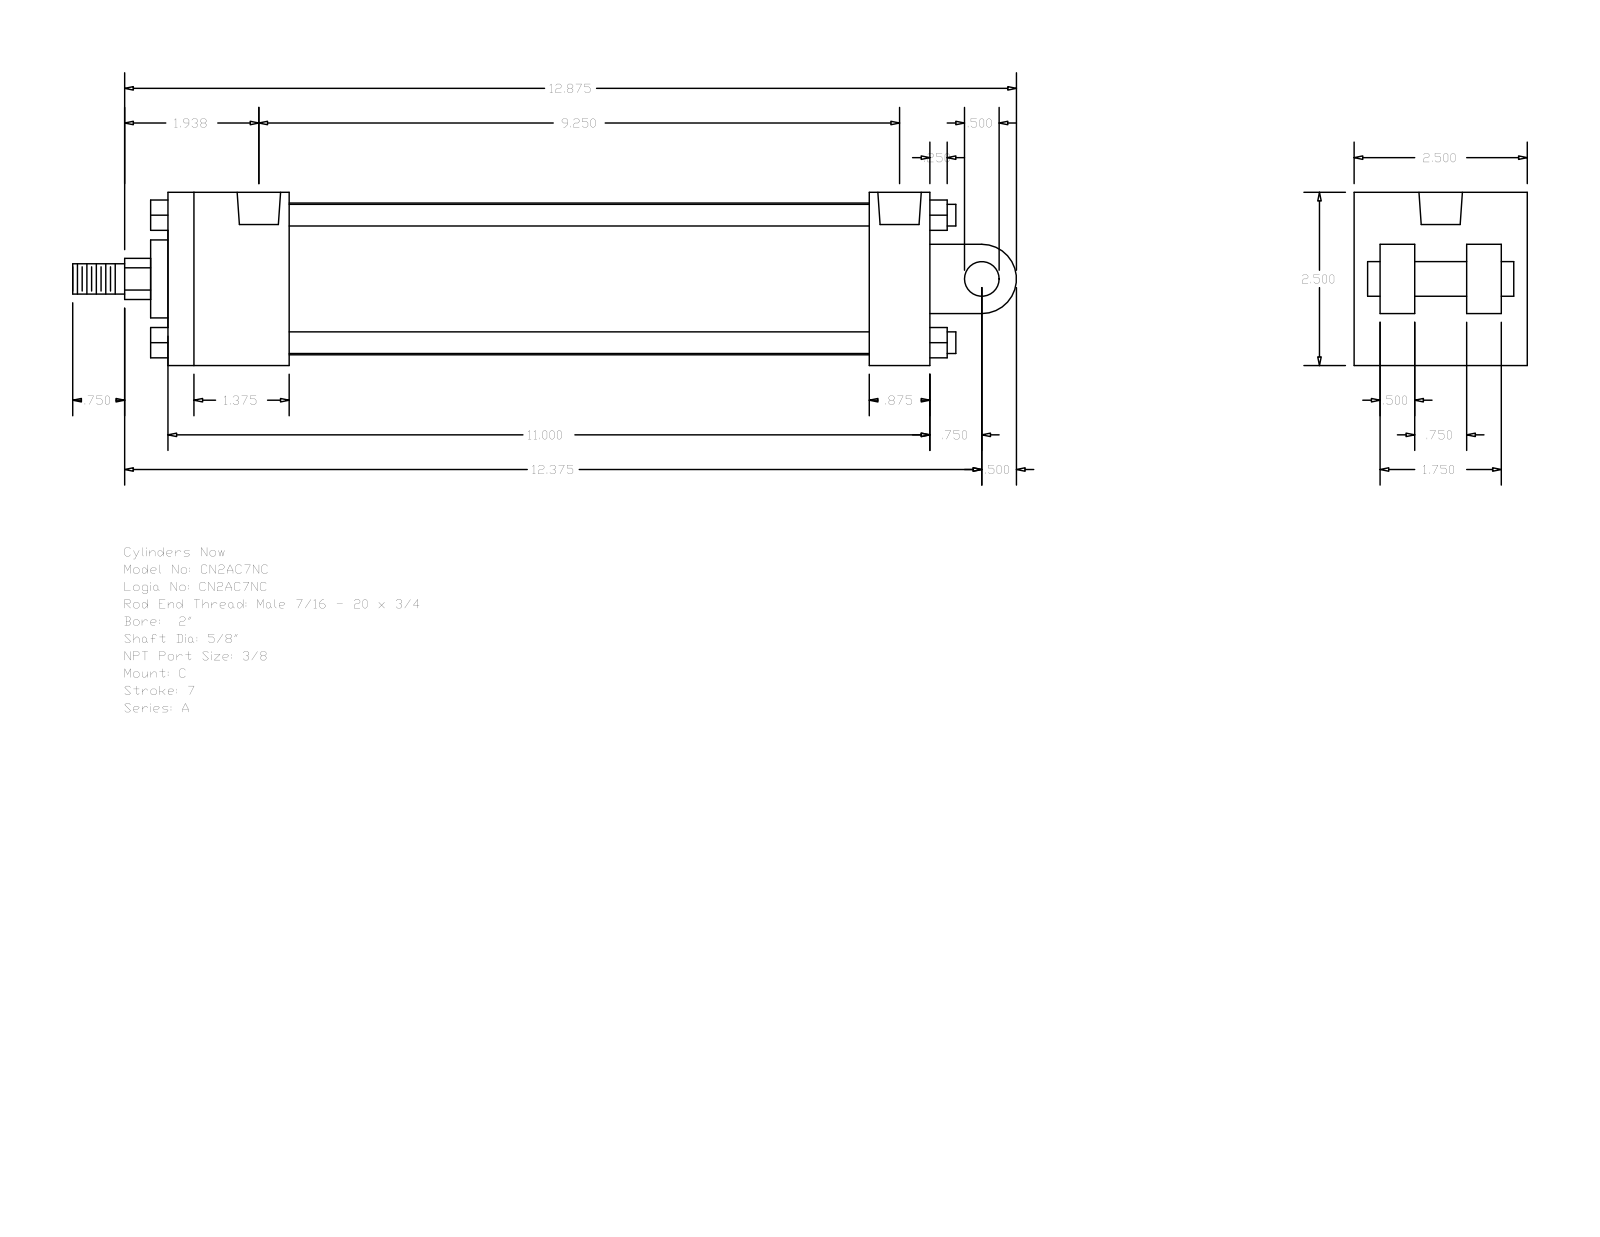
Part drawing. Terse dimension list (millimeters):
name: A_C__0200_0.625
written by: GSSL Pune (CONFIG_CONTROL_DESIGN)
unit: mm
bodies: 0 solids, 135 faces (102 planar, 33 cylindrical, 0 other)
size: 346.07 × 63.5 × 63.5
holes: 4× ⌀5.56, 2× ⌀15.93
bosses: 4× ⌀7.94, 1× ⌀55.63, 1× ⌀28.57, 1× ⌀15.88, 1× ⌀12.7, 1× ⌀11.11
rounds: 1× R7.54, 1× R12.7
face distances: 63.5, 279.39, 22.22, 44.45, 234.94, 257.17, 212.72, 12.7, 6.35, 53.98
hole spacings: 227, 3.97, 3.98, 230.97, 230.98, 234.95
